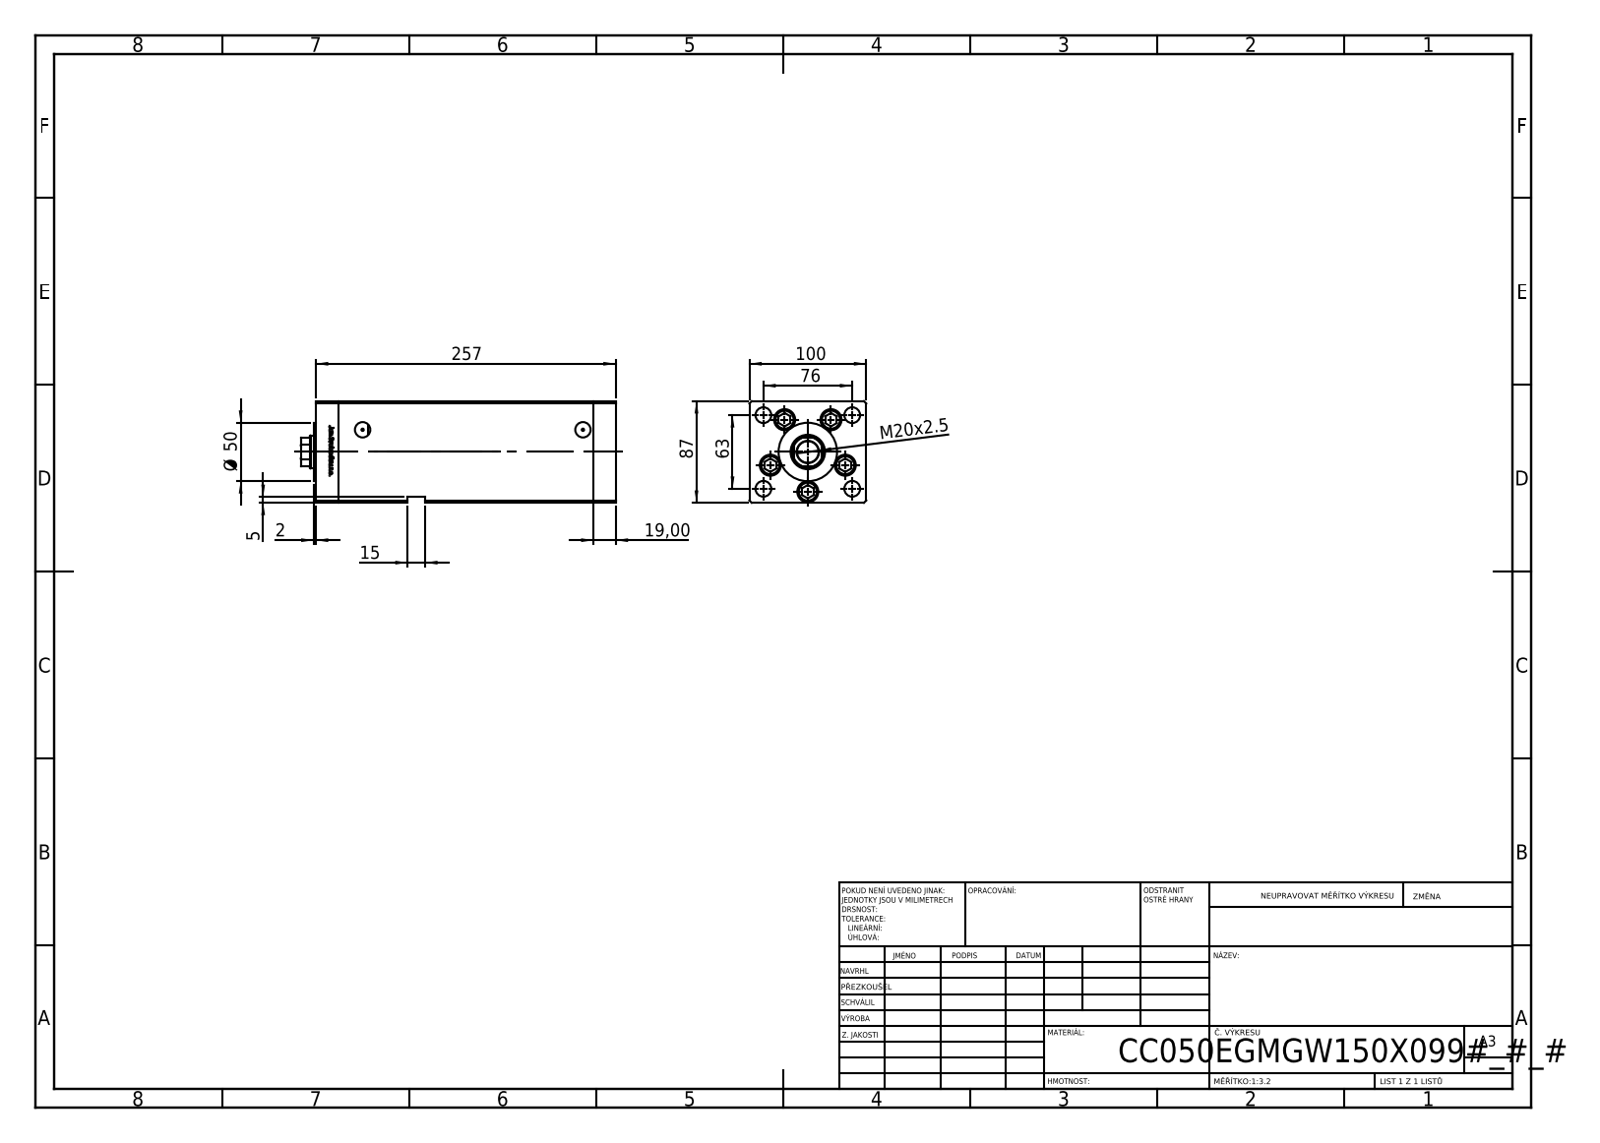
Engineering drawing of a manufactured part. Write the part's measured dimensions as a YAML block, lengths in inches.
part_name: "ALLEN BOLT; V220C_E MIDDLE; V220C_FRONT_E; V220C_VC_E (+1 more)"
step_written_by: "SolidWorks 2019 (CONFIG_CONTROL_DESIGN)"
units: inches
bodies: {solids: 14, faces: 1214, planar: 475, cylindrical: 165, other: 574}
overall_size: [10.61, 3.937, 3.425]
volume: 113.9
surface_area: 411.8
round_holes:
  - {diameter: 0.531, count: 11}
  - {diameter: 0.709, count: 5}
  - {diameter: 0.728, count: 5}
  - {diameter: 0.492, count: 4}
  - {diameter: 0.079, count: 2}
  - {diameter: 0.518, count: 2}
  - {diameter: 1.102, count: 1}
  - {diameter: 1.161, count: 1}
round_bosses_or_shafts:
  - {diameter: 0.669, count: 5}
  - {diameter: 0.315, count: 5}
  - {diameter: 1.969, count: 1}
partial_cylinders:
  - {radius: 0.037, count: 2}
  - {radius: 0.531, count: 1}
face_to_face_distances: [3.937, 3.425, 0.748, 8.602, 9.35, 1.348, 10.098, 0.6, 8.002, 8.75]
hole_center_spacings: [1.339, 0.732, 1.561, 1.943, 2.281, 0.828, 1.499, 1.546]
